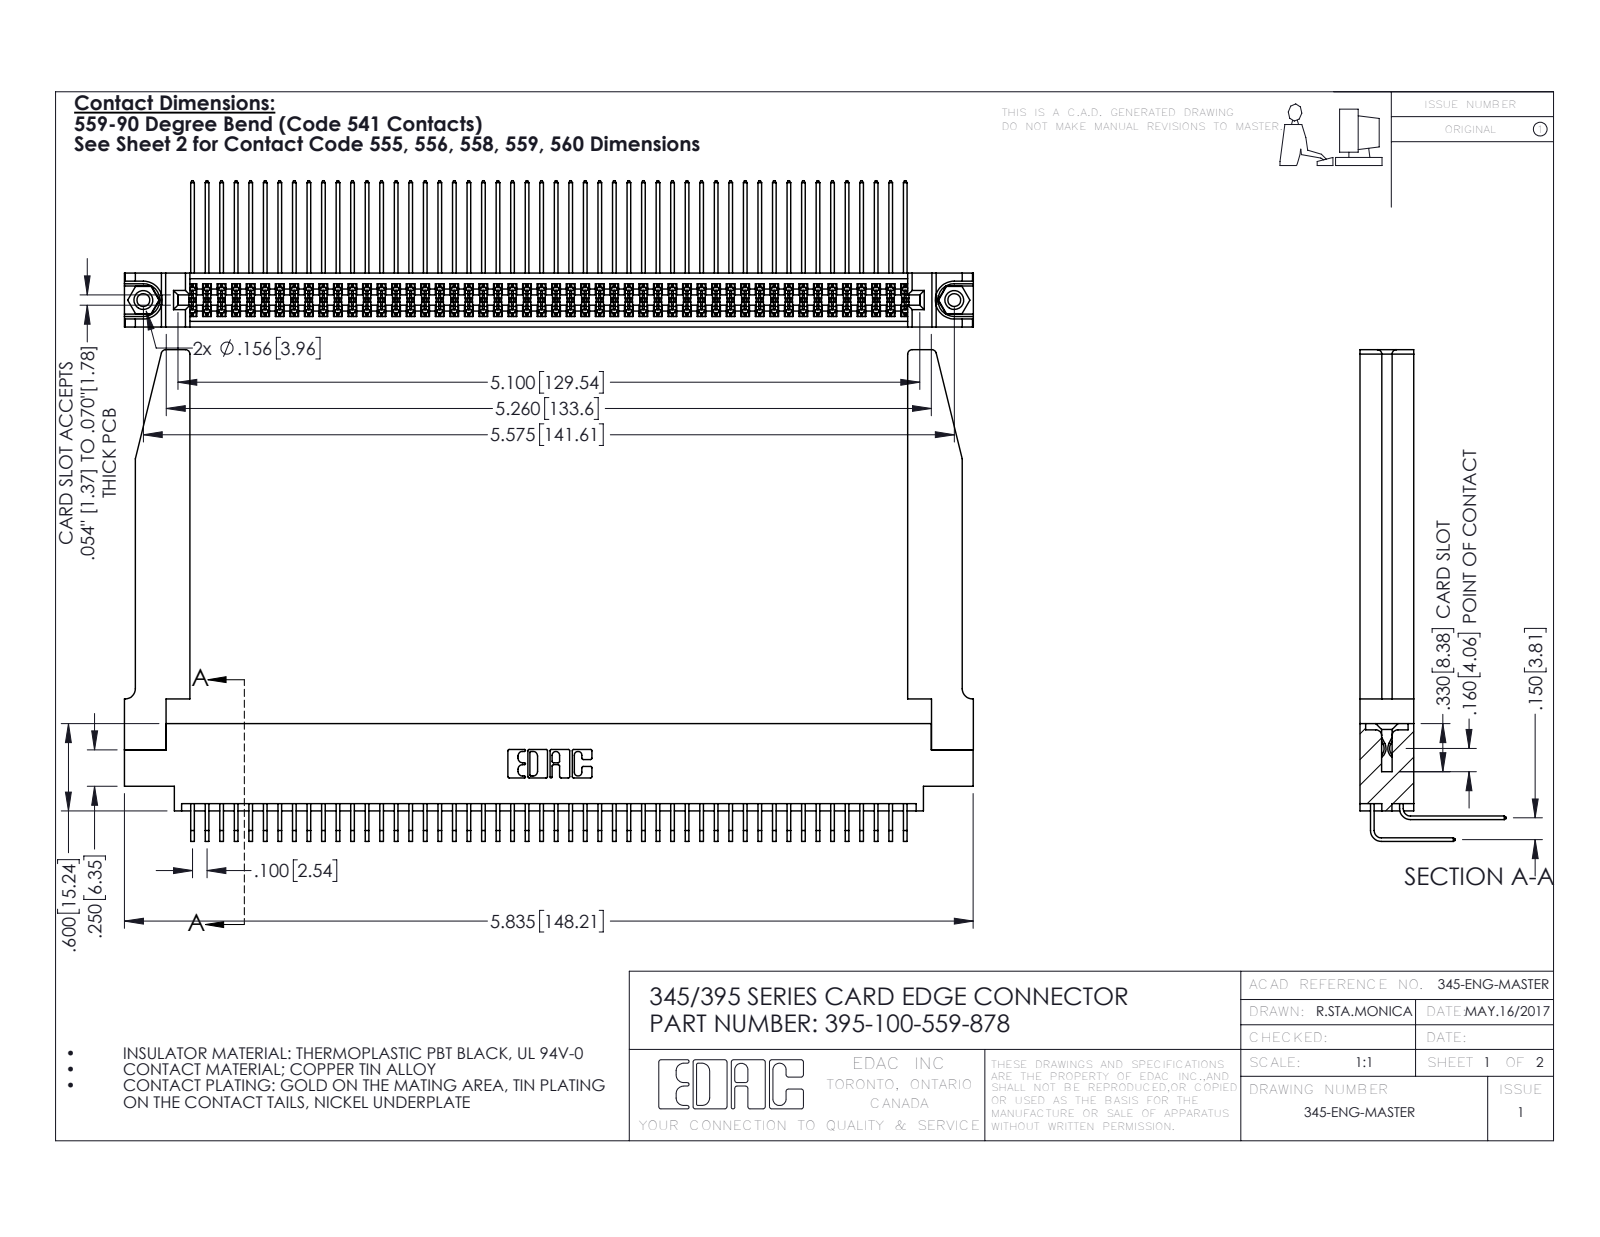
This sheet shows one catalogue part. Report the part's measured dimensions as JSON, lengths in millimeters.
{"part_name": "395-100-559-878; 345-292-001_558 559 Tail - 1; 345-292-001_559 Tail - 2; 345 Part_0.170 Offset - 0.156 Dia-TH (+2 more)", "step_written_by": "SolidWorks 2016 (CONFIG_CONTROL_DESIGN)", "units": "millimeters", "bodies": {"solids": 105, "faces": 5564, "planar": 3726, "cylindrical": 1786, "other": 52}, "overall_size": [148.2, 85.8, 25.5], "volume_mm3": 22710, "surface_area_mm2": 31930, "round_holes": [[2.3, 2], [3.2, 2], [4, 2], [1.6, 1]], "round_bosses_or_shafts": [[3.9, 2]], "partial_cylinders_radius": [[0.2, 151], [0.3, 22], [0.8, 8], [0.2, 6], [0.8, 6], [0.7, 3], [0.4, 2], [0.5, 2]], "face_to_face_distances": [1.8, 9.4, 7.6, 2.5, 6.9, 0.6, 5.1, 5.7, 3.8, 4.4], "hole_center_spacings": [6.9, 135.6, 141.6]}
